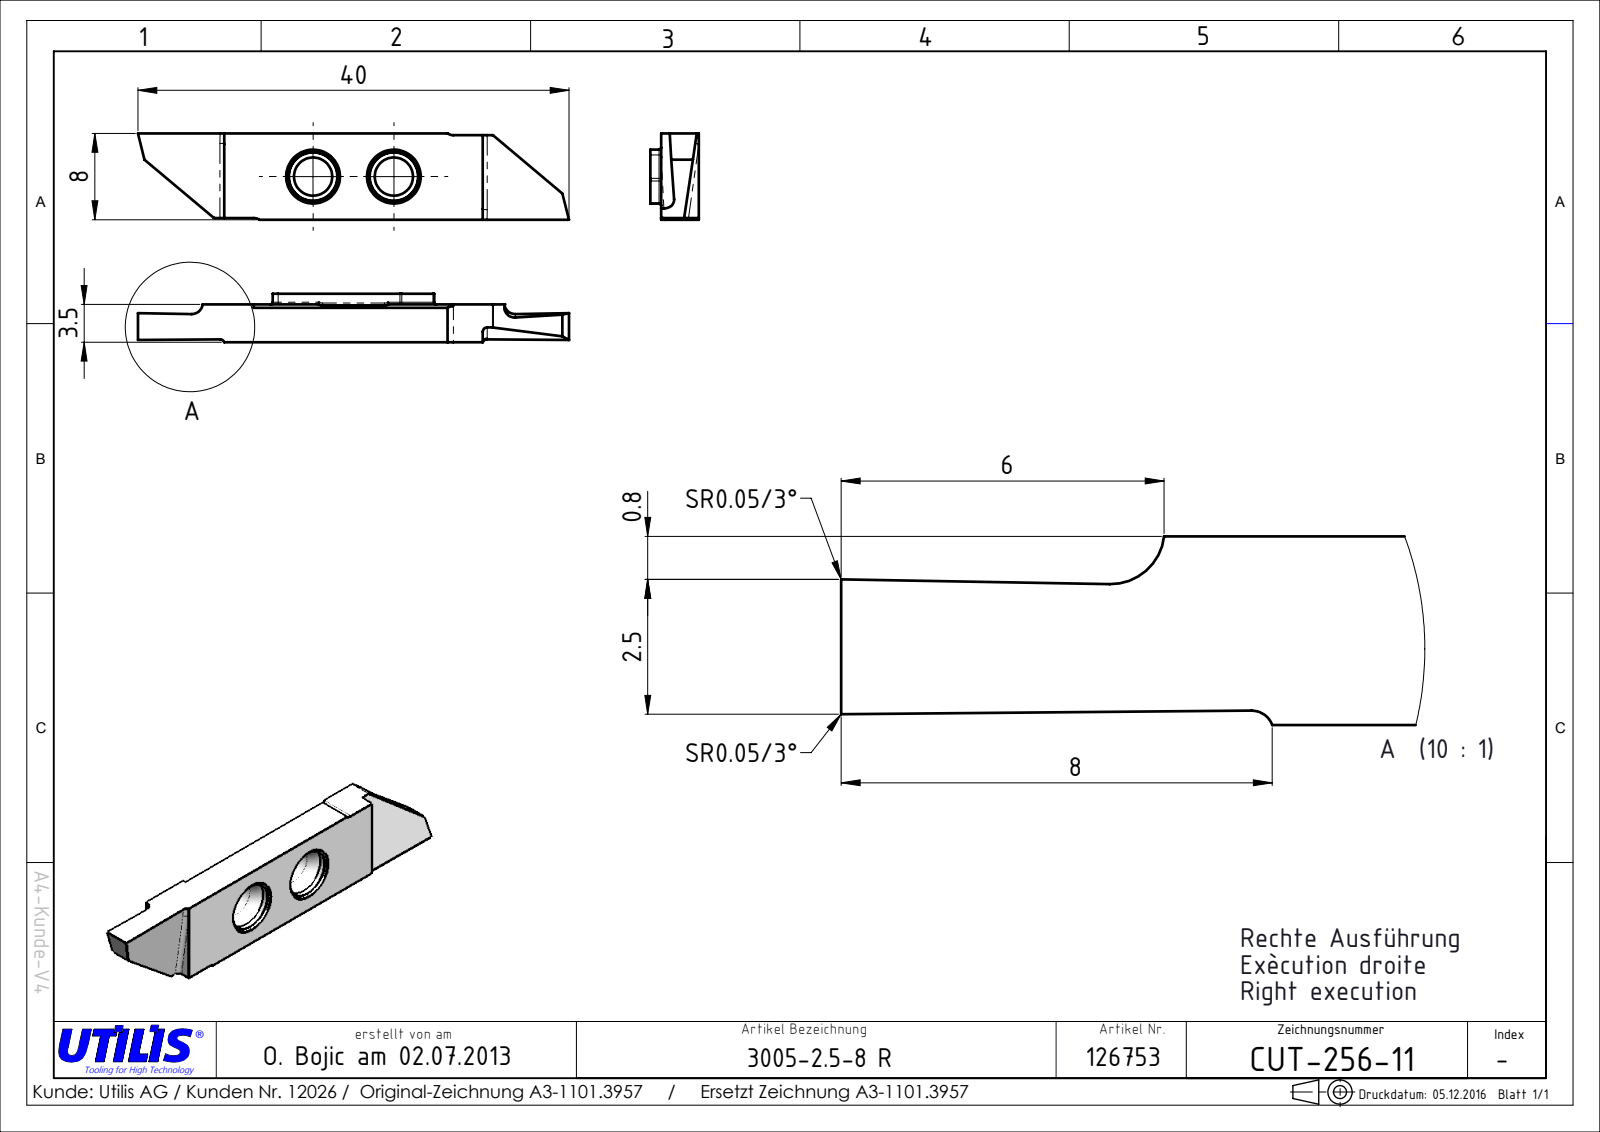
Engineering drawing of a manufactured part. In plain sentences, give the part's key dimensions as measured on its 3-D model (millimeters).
The part is named "CUT-256-11". Its 3-D file was written by "SolidWorks 2016 (AUTOMOTIVE_DESIGN)". It is 1 solid with 36 faces: 22 planar, 14 cylindrical and 0 other. Overall it measures 40 by 8 by 3.5 millimeters. Its volume is 828 cubic millimeters and its surface area 864 square millimeters. Round holes: 2 of diameter 3.55. Partial cylindrical surfaces (rounded edges, fillets, slot ends): 4 of radius 0.15, 4 of radius 1, 2 of radius 0.4. The main face-to-face distances are 3.5, 8, 7.85, 22.54, 7.7, 40, 38.98, 10.75, 29.25, 18.5. The hole center spacings are 7.5.
